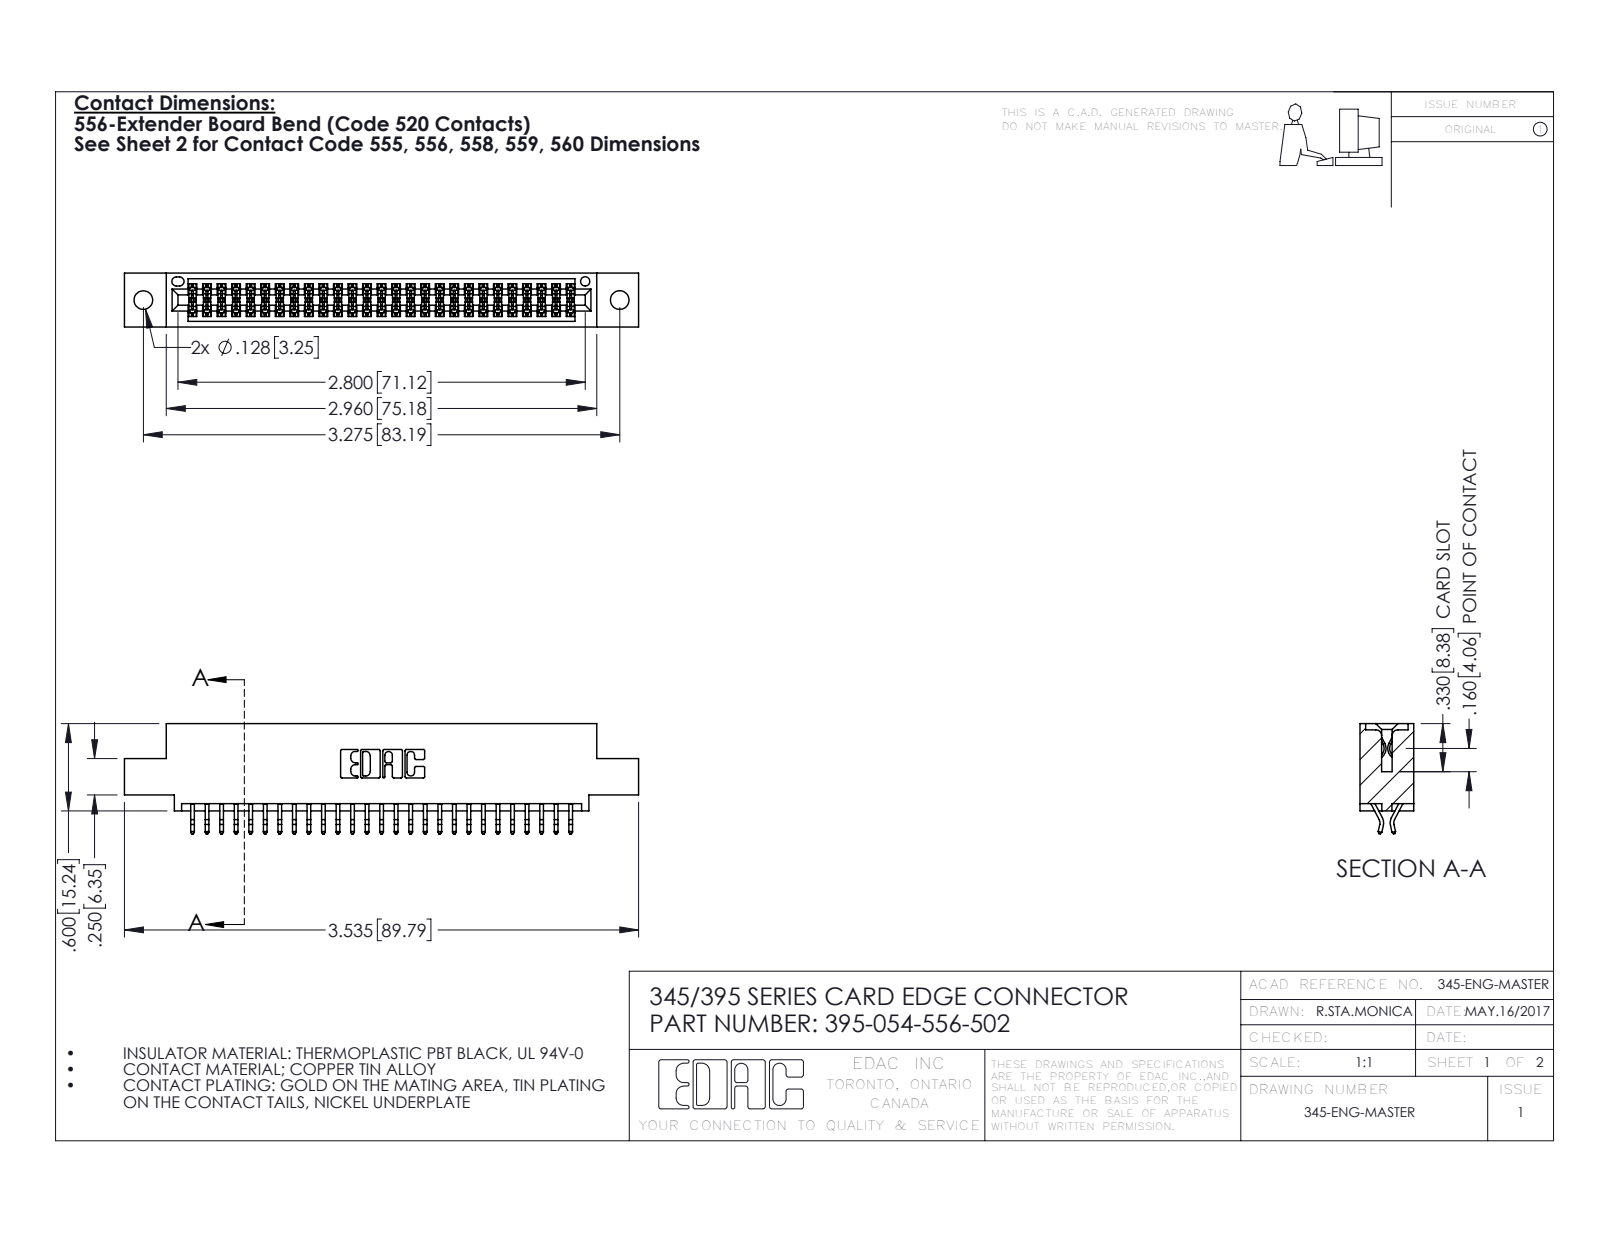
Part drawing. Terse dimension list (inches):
name: 395-054-556-502; 345-292-001_556 Tail; 345 Part_0.110 Offset - 0.128 Dia
written by: SolidWorks 2016 (CONFIG_CONTROL_DESIGN)
unit: in
bodies: 55 solids, 3154 faces (2082 planar, 1072 cylindrical, 0 other)
size: 3.535 × 0.757 × 0.37
volume: 0.517 in³; area: 18.61 in²
holes: 2× ⌀0.128, 1× ⌀0.064
rounds: 81× R0.006, 22× R0.01, 6× R0.007, 6× R0.031, 3× R0.026, 2× R0.01, 2× R0.014, 2× R0.019
face distances: 0.298, 0.072, 0.37, 0.2, 0.025, 0.098, 0.272, 0.225, 0.175, 0.149
hole spacings: 0.27, 3.04, 3.275
